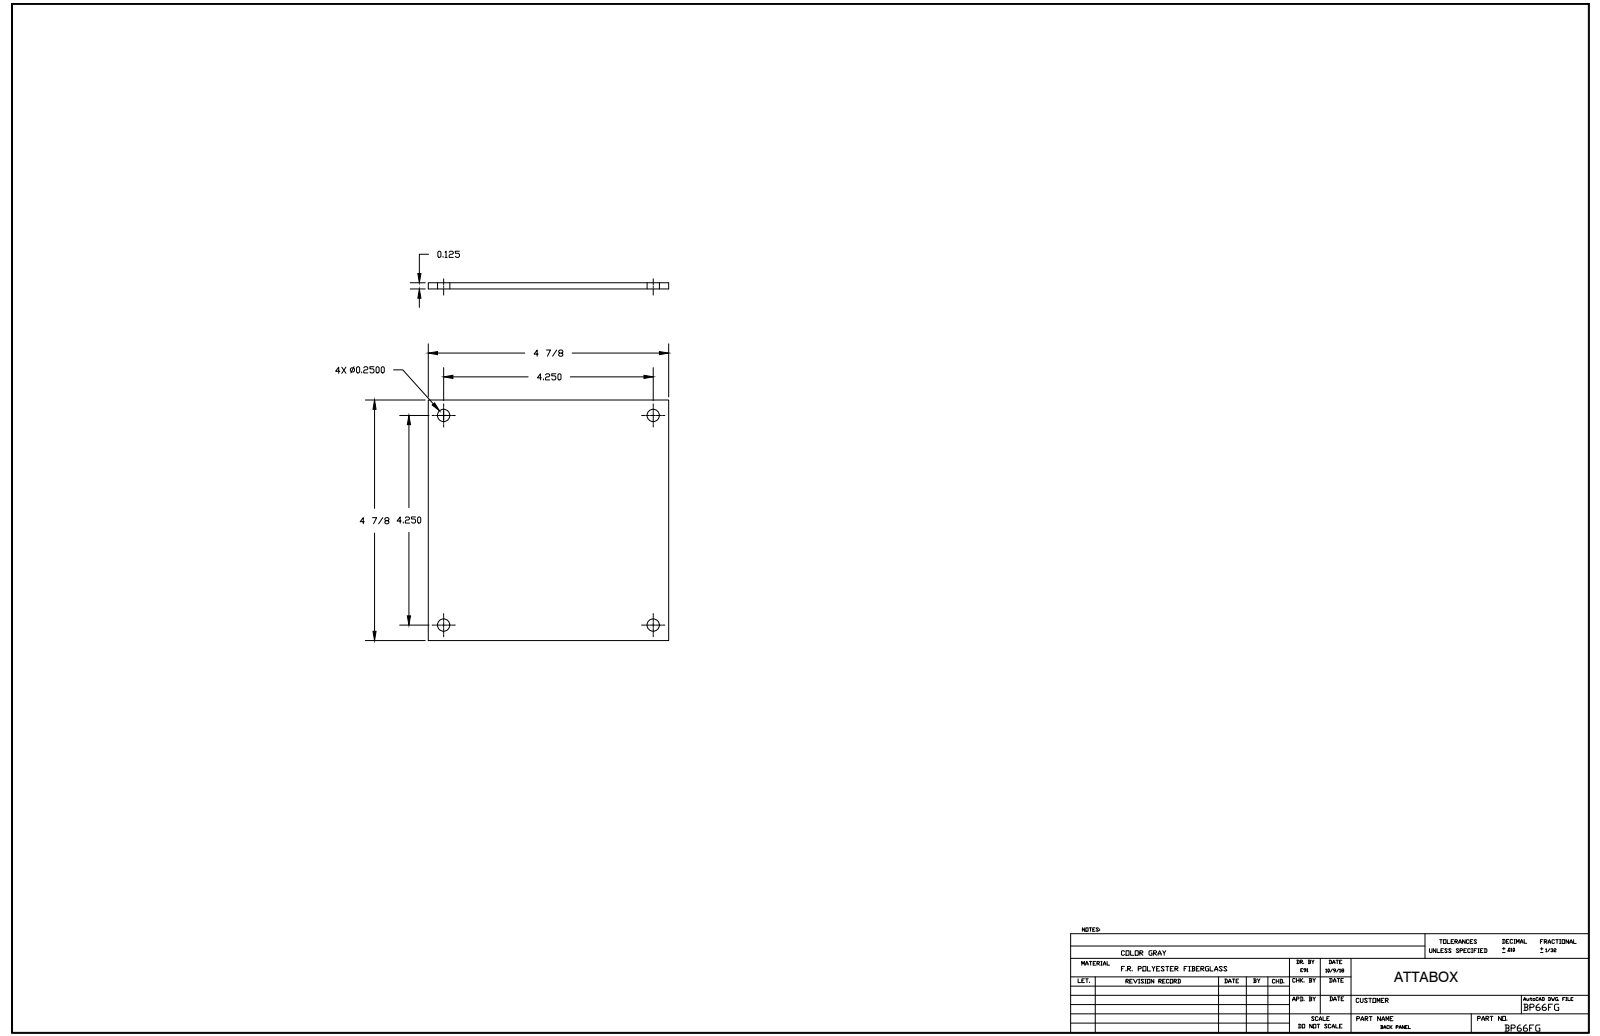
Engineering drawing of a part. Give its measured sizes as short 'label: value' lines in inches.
name: BP66FG_STP
written by: Autodesk Inventor 2014 (AUTOMOTIVE_DESIGN)
unit: in
bodies: 1 solid, 10 faces (6 planar, 4 cylindrical, 0 other)
size: 4.875 × 4.875 × 0.125
volume: 2.946 in³; area: 49.97 in²
holes: 4× ⌀0.25
face distances: 0.125, 4.875
hole spacings: 4.25, 6.01
